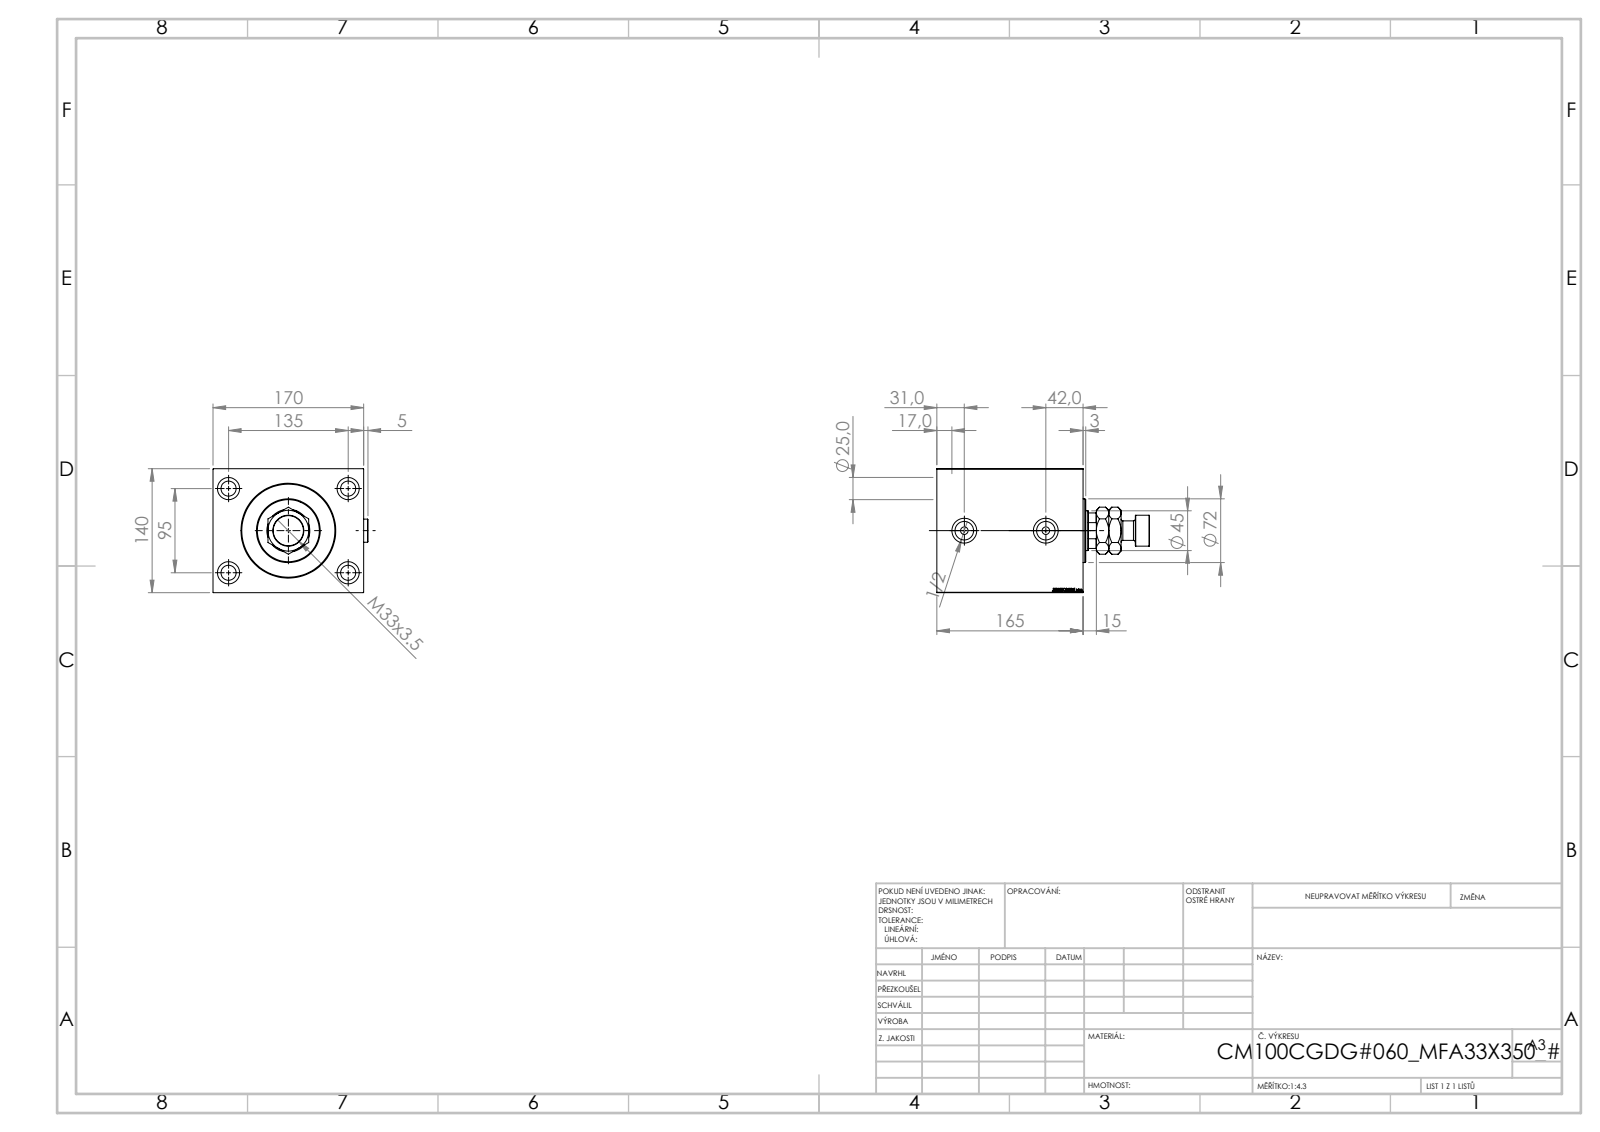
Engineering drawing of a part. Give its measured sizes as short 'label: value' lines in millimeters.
name: V450CM_VC_B; MFA; V450CM_C_VCP; V450CM_C_Body (+1 more)
written by: SolidWorks 2019 (CONFIG_CONTROL_DESIGN)
unit: mm
bodies: 6 solids, 971 faces (459 planar, 82 cylindrical, 430 other)
size: 240 × 174.9 × 140
volume: 3 416 000 mm³; area: 324 966 mm²
holes: 4× ⌀17, 4× ⌀25, 2× ⌀8.5, 2× ⌀20.96, 2× ⌀28, 1× ⌀31.5, 1× ⌀45, 1× ⌀48.5, 1× ⌀100, 1× ⌀102, 1× ⌀105
bosses: 2× ⌀26, 1× ⌀72, 1× ⌀35, 1× ⌀22
rounds: 1× R22
face distances: 140, 170, 165, 139, 26, 90, 15, 60, 150, 75
hole spacings: 82.54, 95, 135, 165.08, 92
